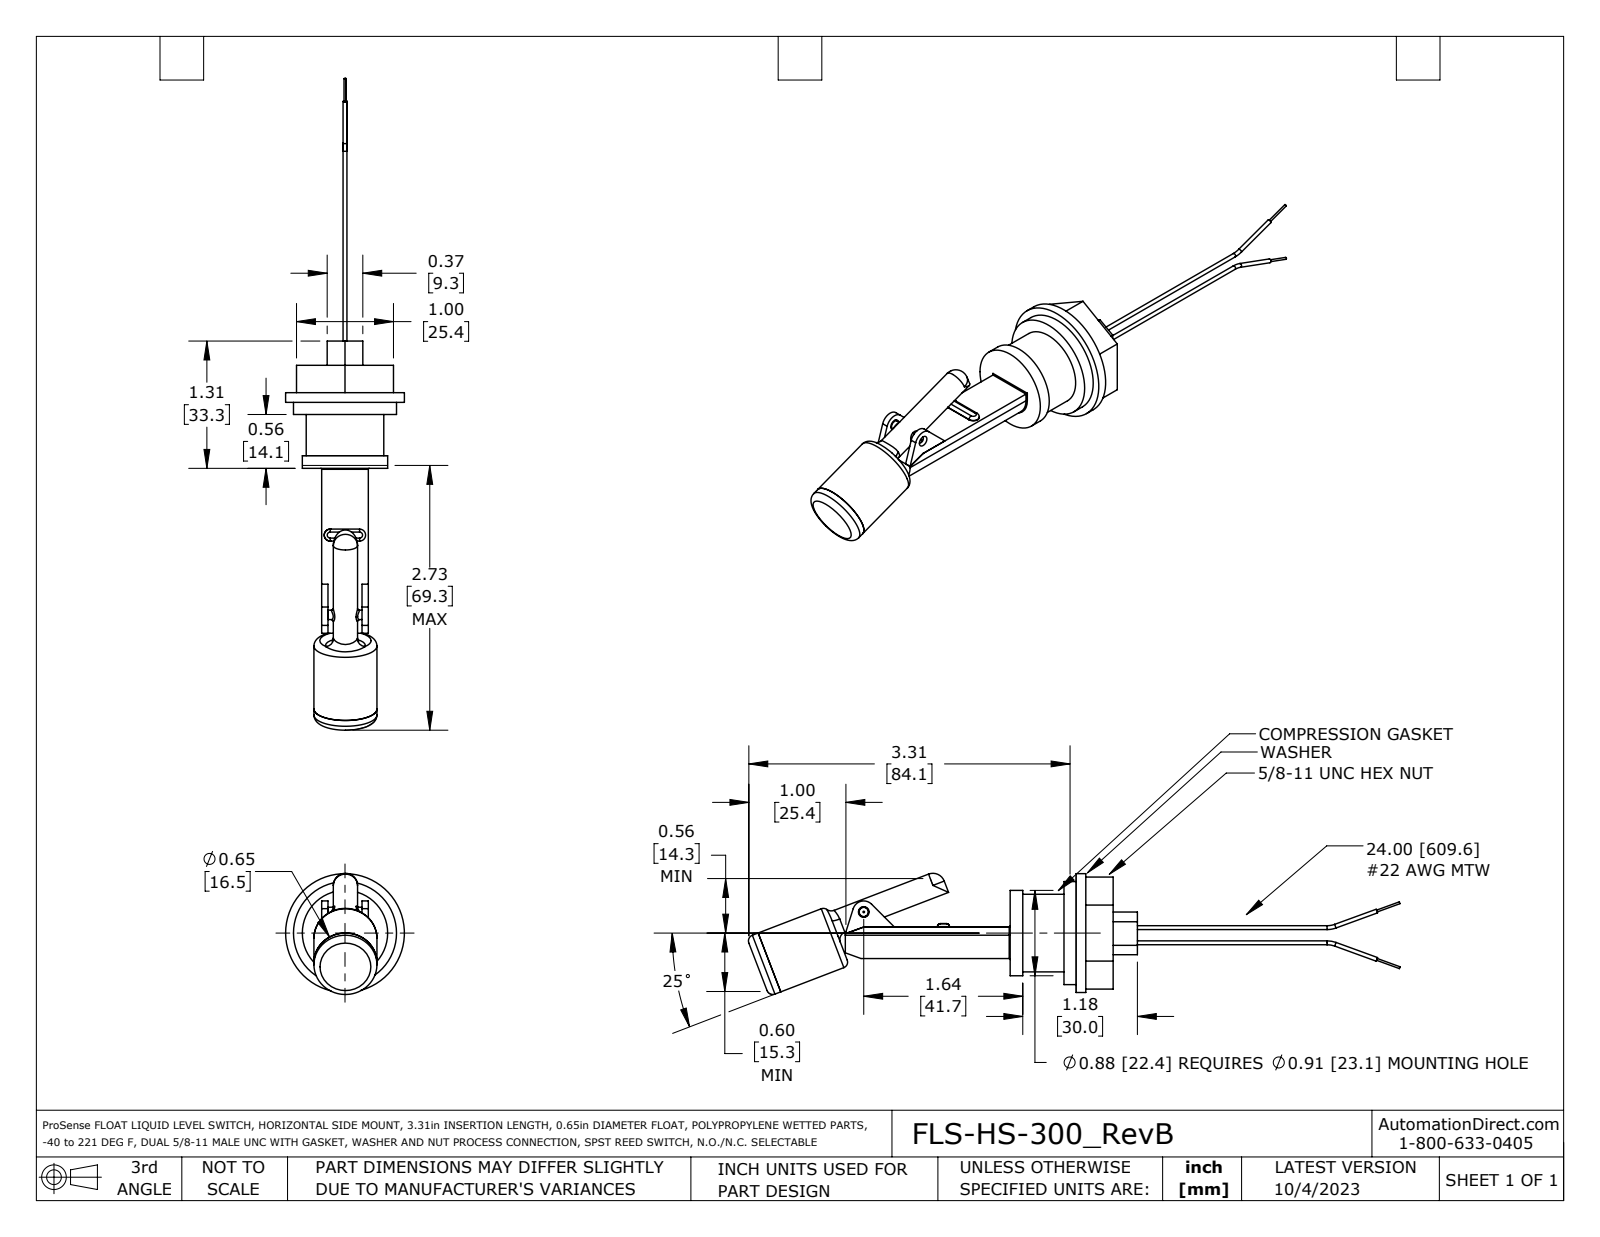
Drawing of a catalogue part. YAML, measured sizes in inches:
part_name: "M8790-14-4184_FLS-HS-300 nc sr1 coord"
step_written_by: "SolidWorks 2021 (AUTOMOTIVE_DESIGN)"
units: inches
bodies: {solids: 12, faces: 202, planar: 71, cylindrical: 73, other: 58}
overall_size: [6.719, 1.249, 1.225]
volume: 1.114
surface_area: 25.15
round_holes:
  - {diameter: 0.01, count: 2}
  - {diameter: 0.11, count: 1}
  - {diameter: 0.45, count: 1}
  - {diameter: 0.5, count: 1}
  - {diameter: 0.53, count: 1}
  - {diameter: 0.56, count: 1}
  - {diameter: 0.625, count: 1}
  - {diameter: 0.643, count: 1}
round_bosses_or_shafts:
  - {diameter: 0.04, count: 4}
  - {diameter: 0.65, count: 2}
  - {diameter: 0.02, count: 2}
  - {diameter: 1.225, count: 1}
  - {diameter: 1.063, count: 1}
  - {diameter: 0.88, count: 1}
  - {diameter: 0.8, count: 1}
  - {diameter: 0.55, count: 1}
partial_cylinders:
  - {radius: 0.01, count: 3}
  - {radius: 0.031, count: 2}
  - {radius: 0.062, count: 2}
  - {radius: 0.18, count: 2}
  - {radius: 0.1, count: 1}
  - {radius: 0.114, count: 1}
  - {radius: 0.125, count: 1}
  - {radius: 0.223, count: 1}
face_to_face_distances: [0.1, 0.382, 0.282, 0.55, 0.65, 0.932, 1, 0.13, 0.68, 0.78]
hole_center_spacings: [0.056, 0.1, 0.156]
